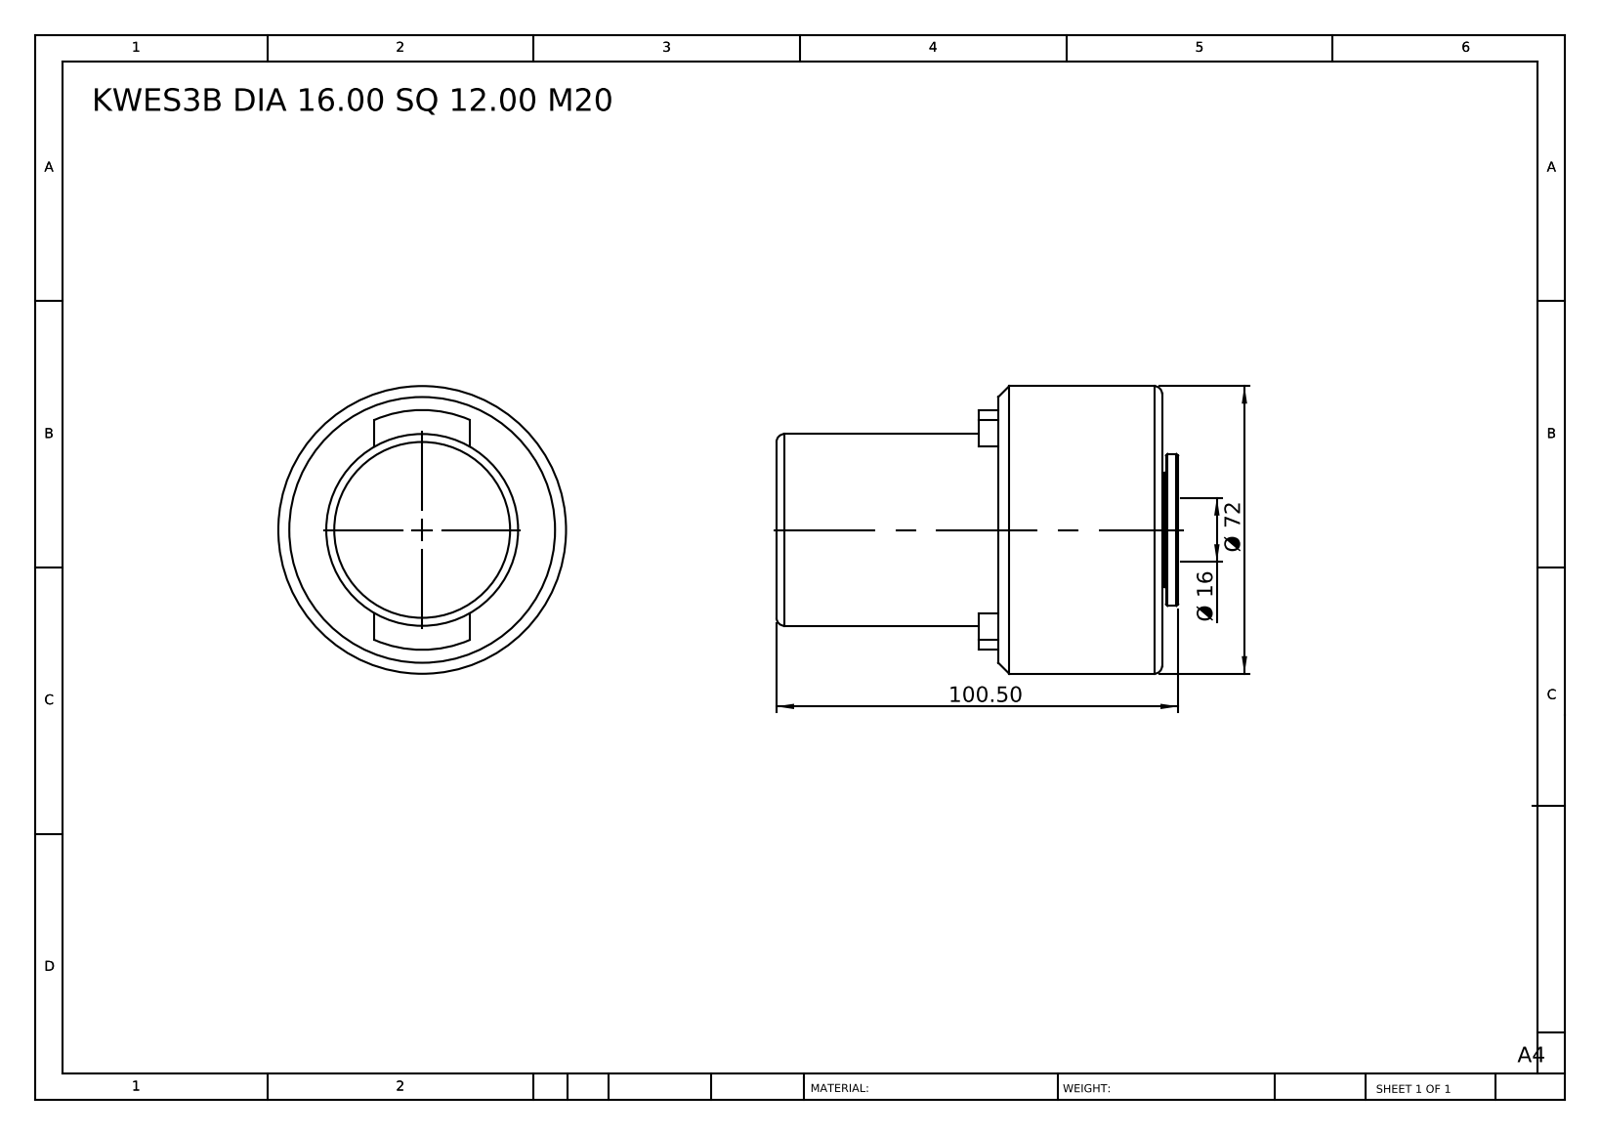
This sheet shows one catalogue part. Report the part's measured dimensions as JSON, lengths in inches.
{"part_name": "KWES3B DIA 16.00 SQ 12.00 M20", "step_written_by": "SolidWorks 2014 (CONFIG_CONTROL_DESIGN)", "units": "inches", "bodies": {"solids": 1, "faces": 39, "planar": 12, "cylindrical": 13, "other": 14}, "overall_size": [3.957, 2.835, 2.835], "volume_in3": 16.09, "surface_area_in2": 44.3, "round_holes": [[0.63, 1]], "round_bosses_or_shafts": [[2.835, 1], [1.89, 1], [1.496, 1], [1.122, 1]], "partial_cylinders_radius": [[1.181, 1]], "face_to_face_distances": [3.799, 2.185, 1.614, 3.957, 1.772, 0.157, 0.197, 3.839, 1.654, 0.039]}
